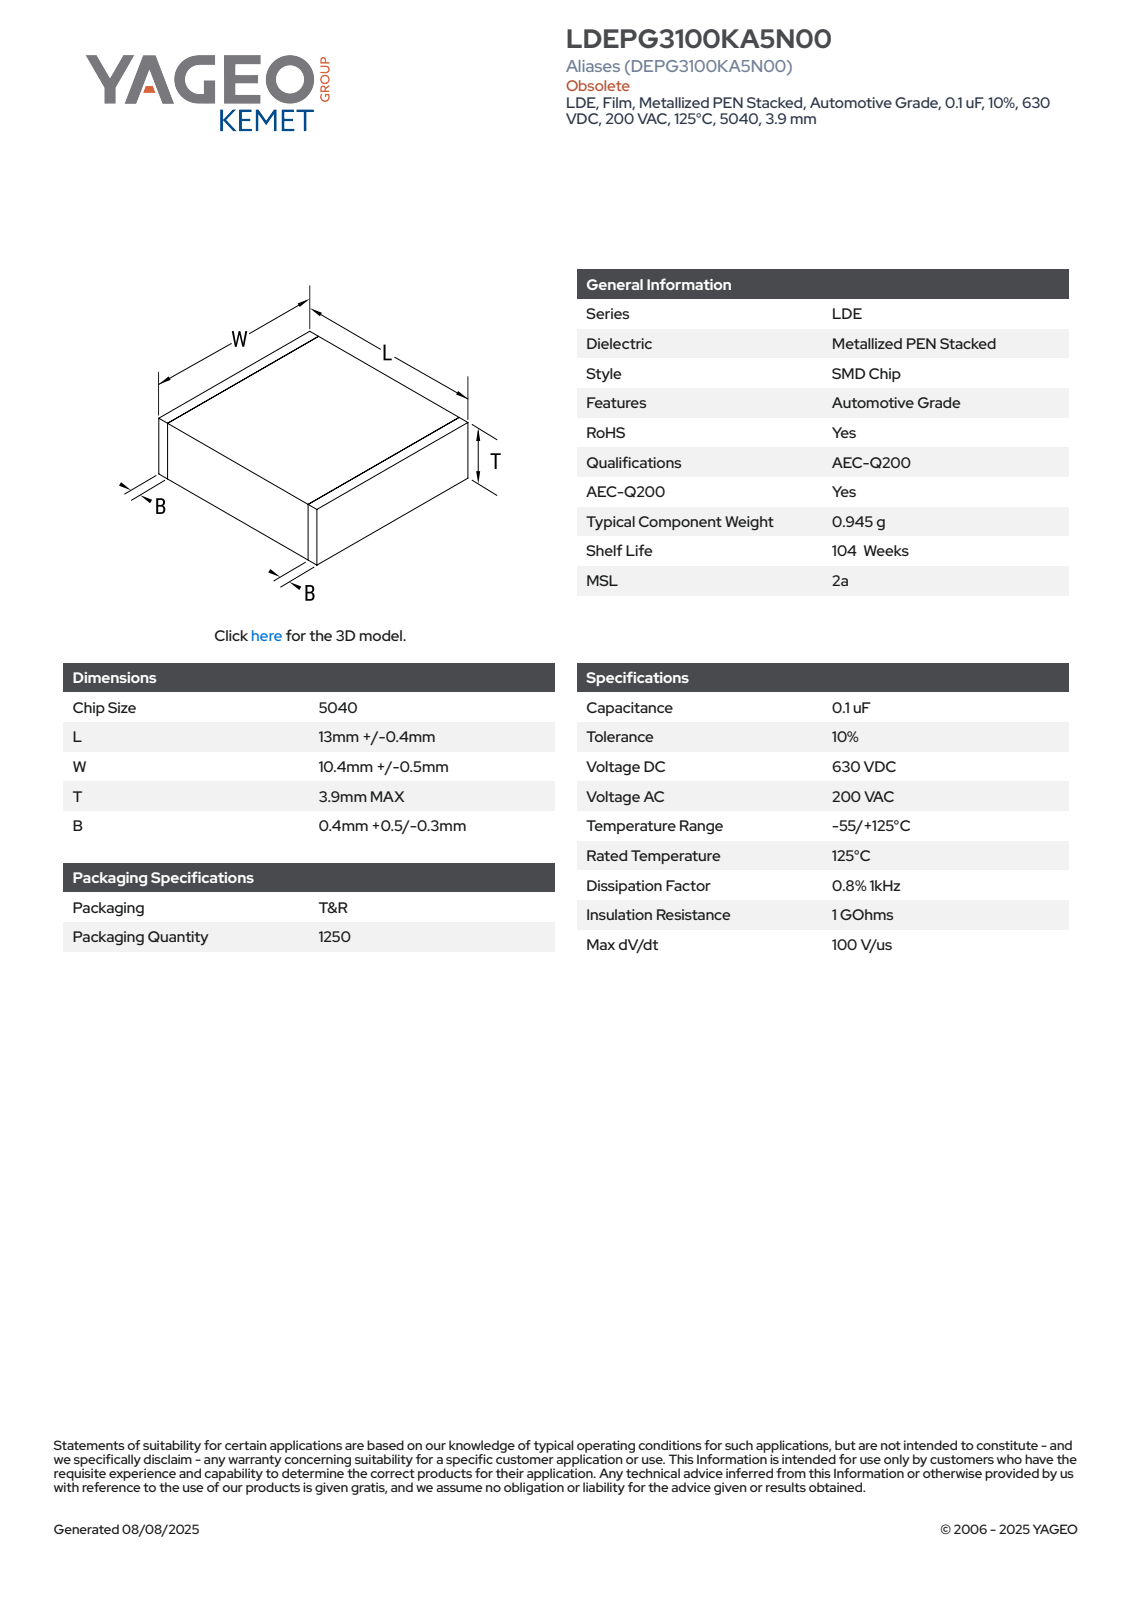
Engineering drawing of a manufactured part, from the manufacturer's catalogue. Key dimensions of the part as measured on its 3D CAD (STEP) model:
Part name (STEP PRODUCT): CFS_LDELDB_5040_L13.4W10.9T3.9B0.9
STEP written by: SolidWorks 2020 (AUTOMOTIVE_DESIGN)
Units: millimetres
Bodies: 4 solids, 73 faces (73 planar, 0 cylindrical, 0 other)
Overall size (bounding box): 13.4 × 10.9 × 3.9
Volume: 566 mm³ · Surface area: 490 mm²
Main face-to-face distances: 3.88, 10.88, 13.4, 3.89, 3.9, 10.89, 10.9, 0.5, 12.9, 12.4
